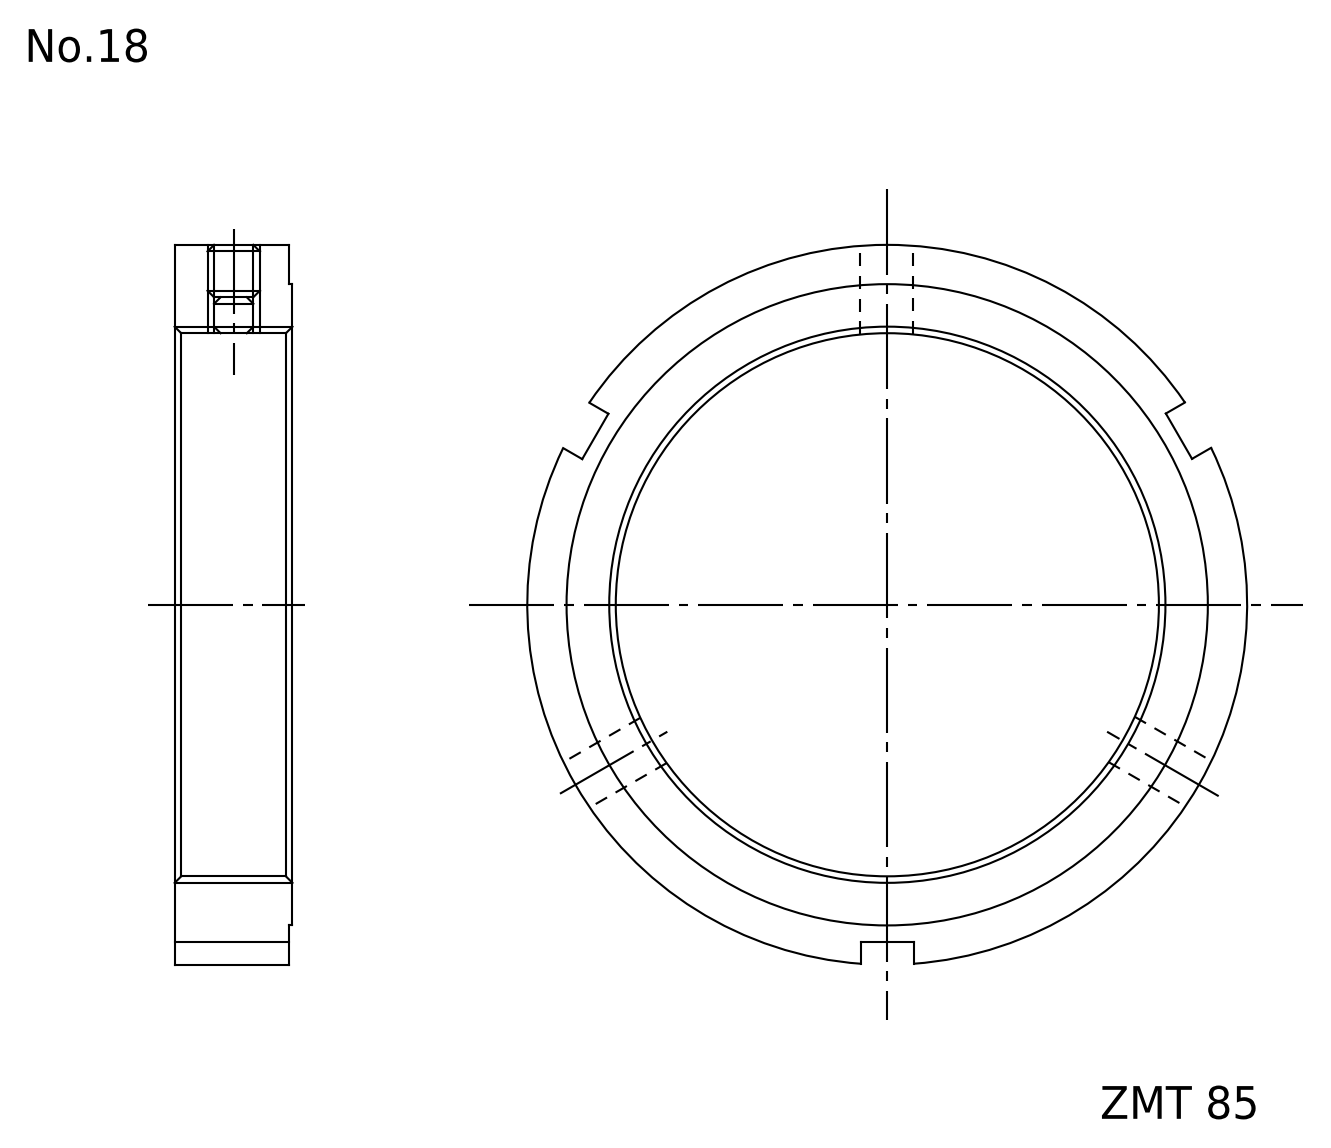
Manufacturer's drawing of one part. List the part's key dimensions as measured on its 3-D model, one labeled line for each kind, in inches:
Part name (STEP PRODUCT): FKD ZMT 85
STEP written by: Autodesk Inventor 2011 (AUTOMOTIVE_DESIGN)
Units: inches
Bodies: 1 solid, 20 faces (12 planar, 8 cylindrical, 0 other)
Overall size (bounding box): 4.331 × 4.325 × 0.709
Volume: 3.997 in³ · Surface area: 30.12 in²
Round holes (diameter × count): ⌀0.262 ×3, ⌀3.346 ×1
Round bosses / shafts (diameter × count): ⌀4.331 ×1, ⌀4.016 ×1
Main face-to-face distances: 0.709, 0.02, 0.689, 0.315
